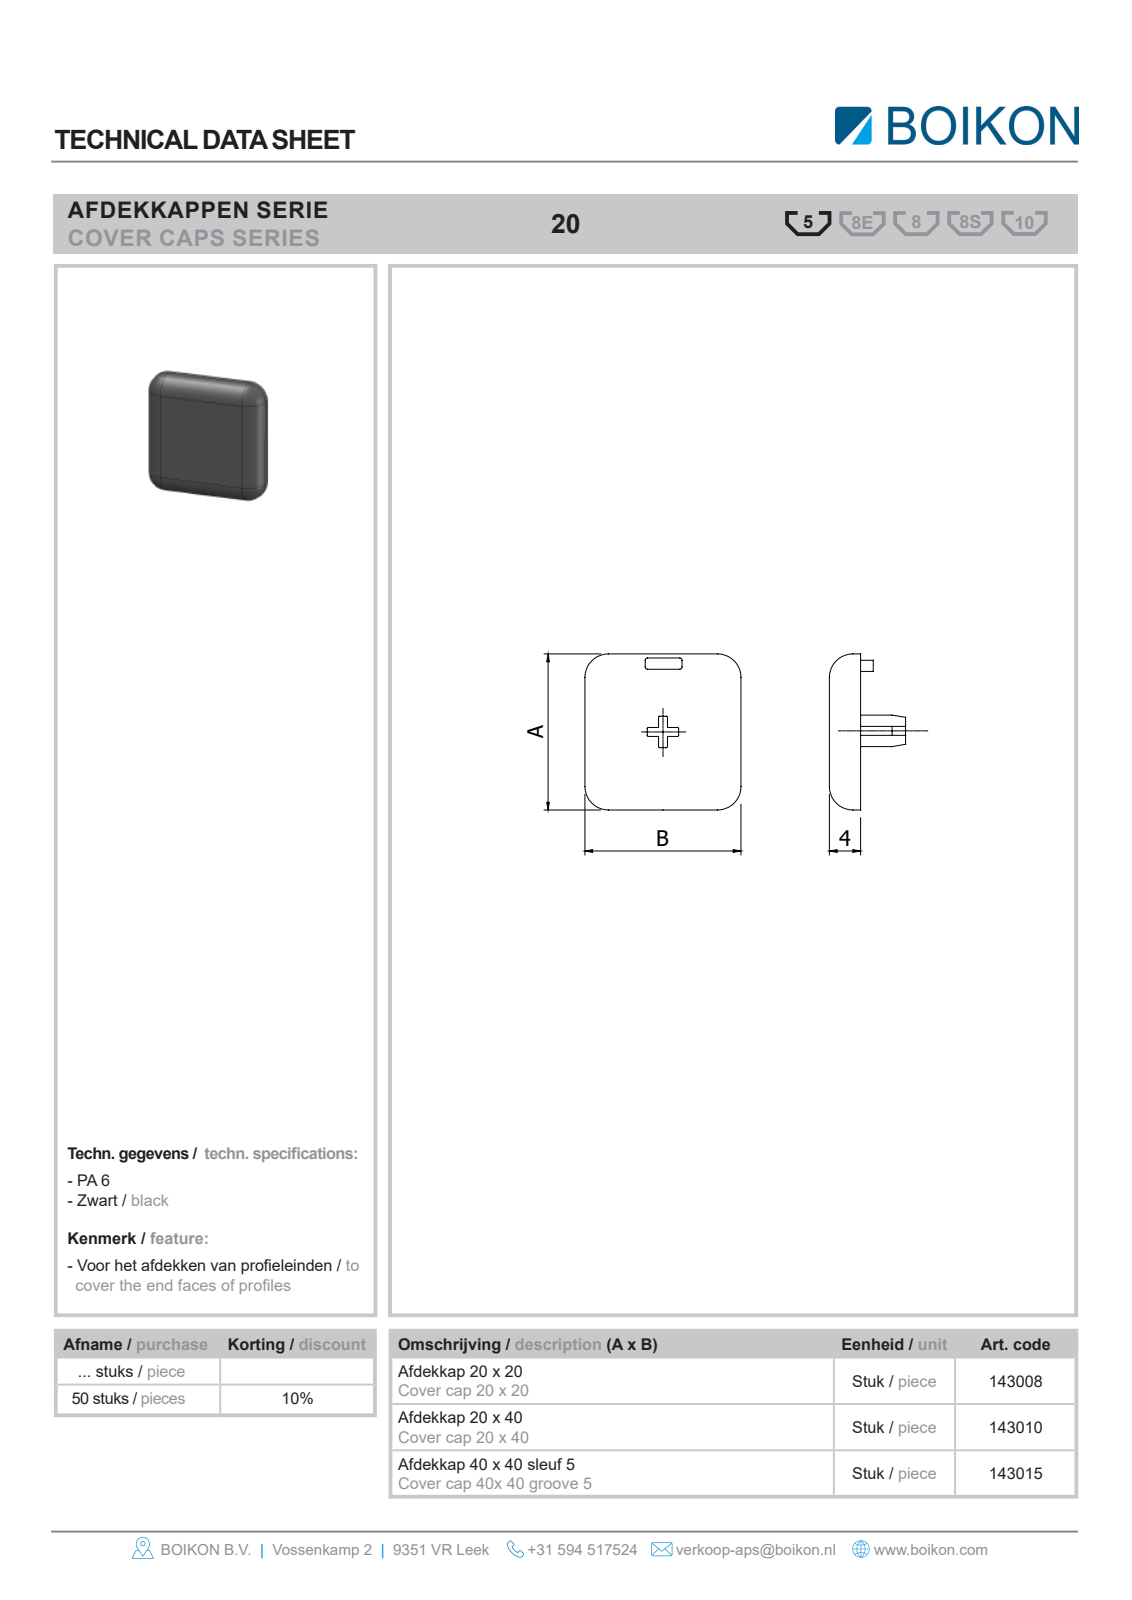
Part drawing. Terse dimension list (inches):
name: Root; 143010 Afdekkap 20 x 40BOIKON
written by: HiCAD 2013 1802.4 Build 509 (AUTOMOTIVE_DESIGN)
unit: in
bodies: 1 solid, 18 faces (6 planar, 8 cylindrical, 4 other)
size: 1.575 × 0.787 × 0.157
volume: 0.18 in³; area: 2.933 in²
rounds: 8× R0.118
face distances: 0.157, 0.787, 1.575
